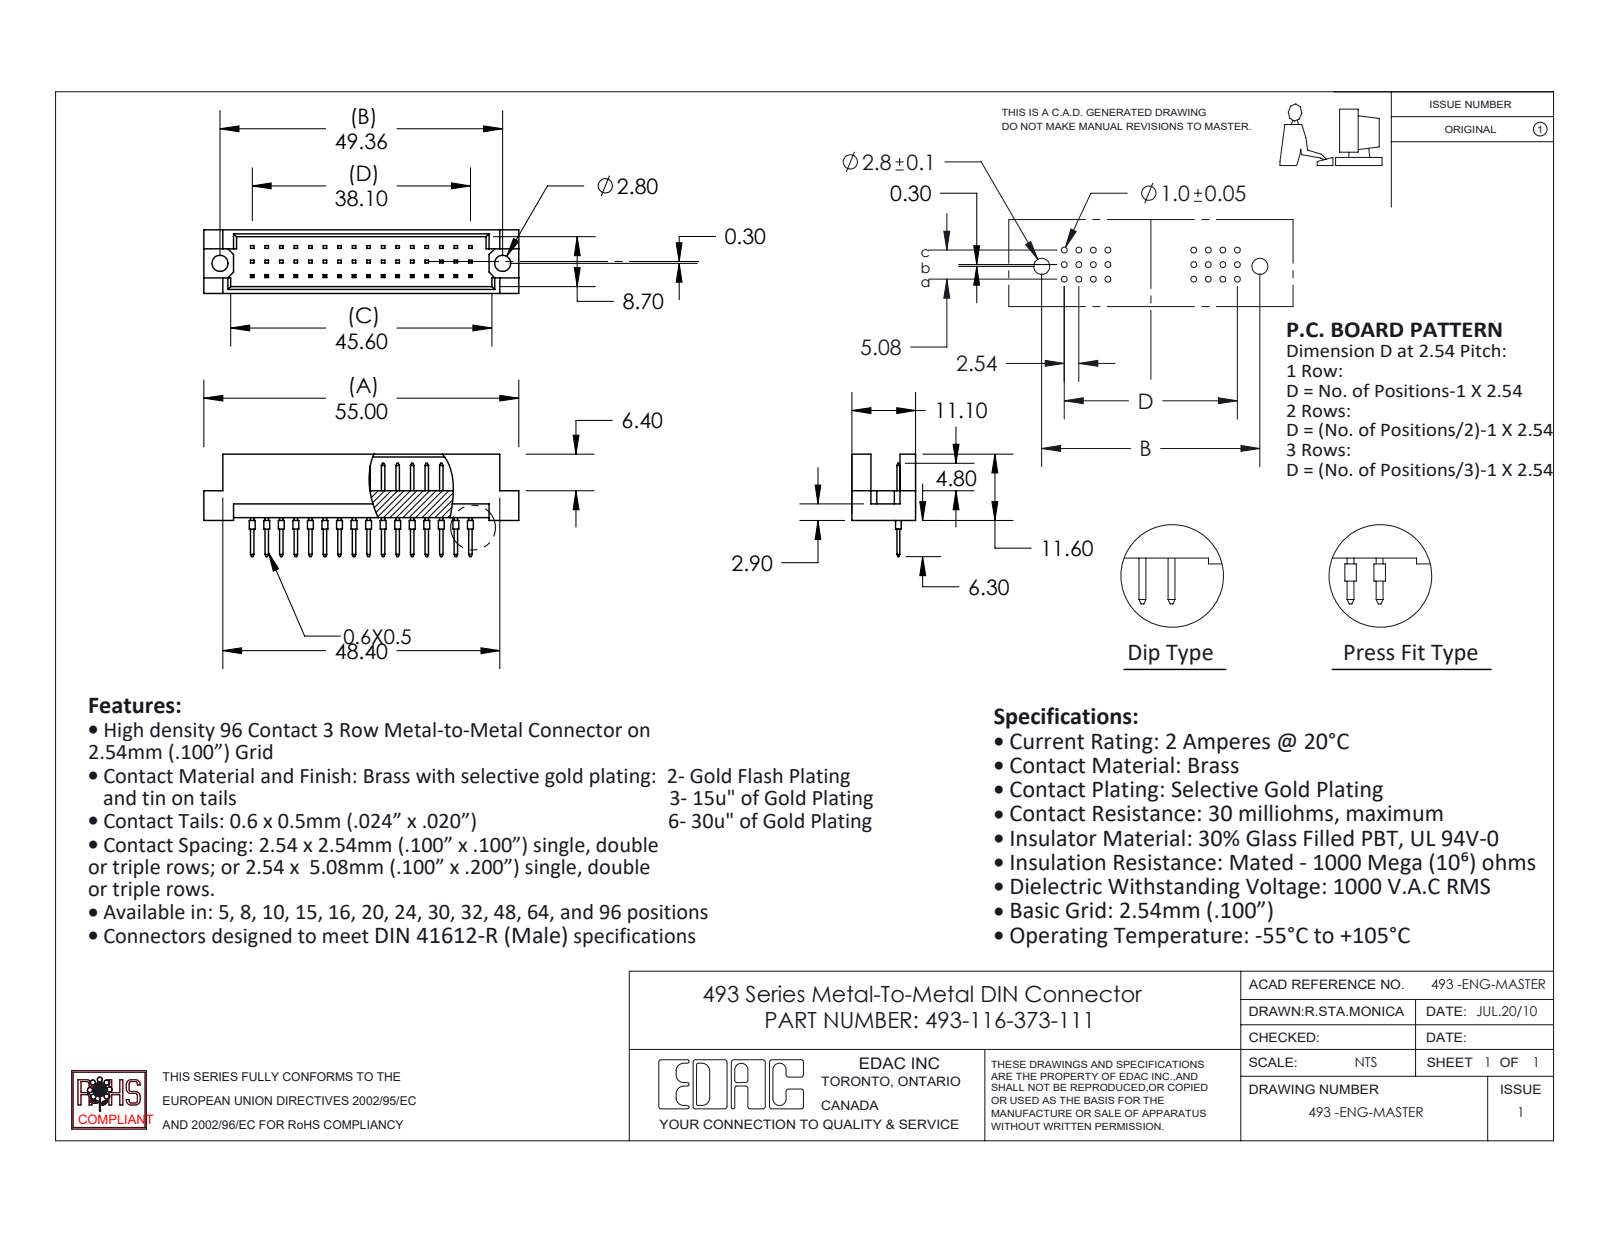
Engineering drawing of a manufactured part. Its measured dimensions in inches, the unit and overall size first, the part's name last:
Units: inches
Overall size (bounding box): 2.165 × 0.705 × 0.437
Round holes (diameter × count): ⌀0.11 ×2
Round bosses / shafts (diameter × count): ⌀0.039 ×16
Main face-to-face distances: 0.047, 0.39, 0.437, 0.343, 0.02, 0.185, 0.1, 0.2, 0.109, 0.328
Hole centre spacings: 1.943
Volume: 0.205 in³ · Surface area: 6.761 in²
Bodies: 17 solids, 596 faces (560 planar, 36 cylindrical, 0 other)
Part name (STEP PRODUCT): 493-290_73; 493-116-373-112; 493 Part_48
STEP written by: SolidWorks 2020 (CONFIG_CONTROL_DESIGN)
